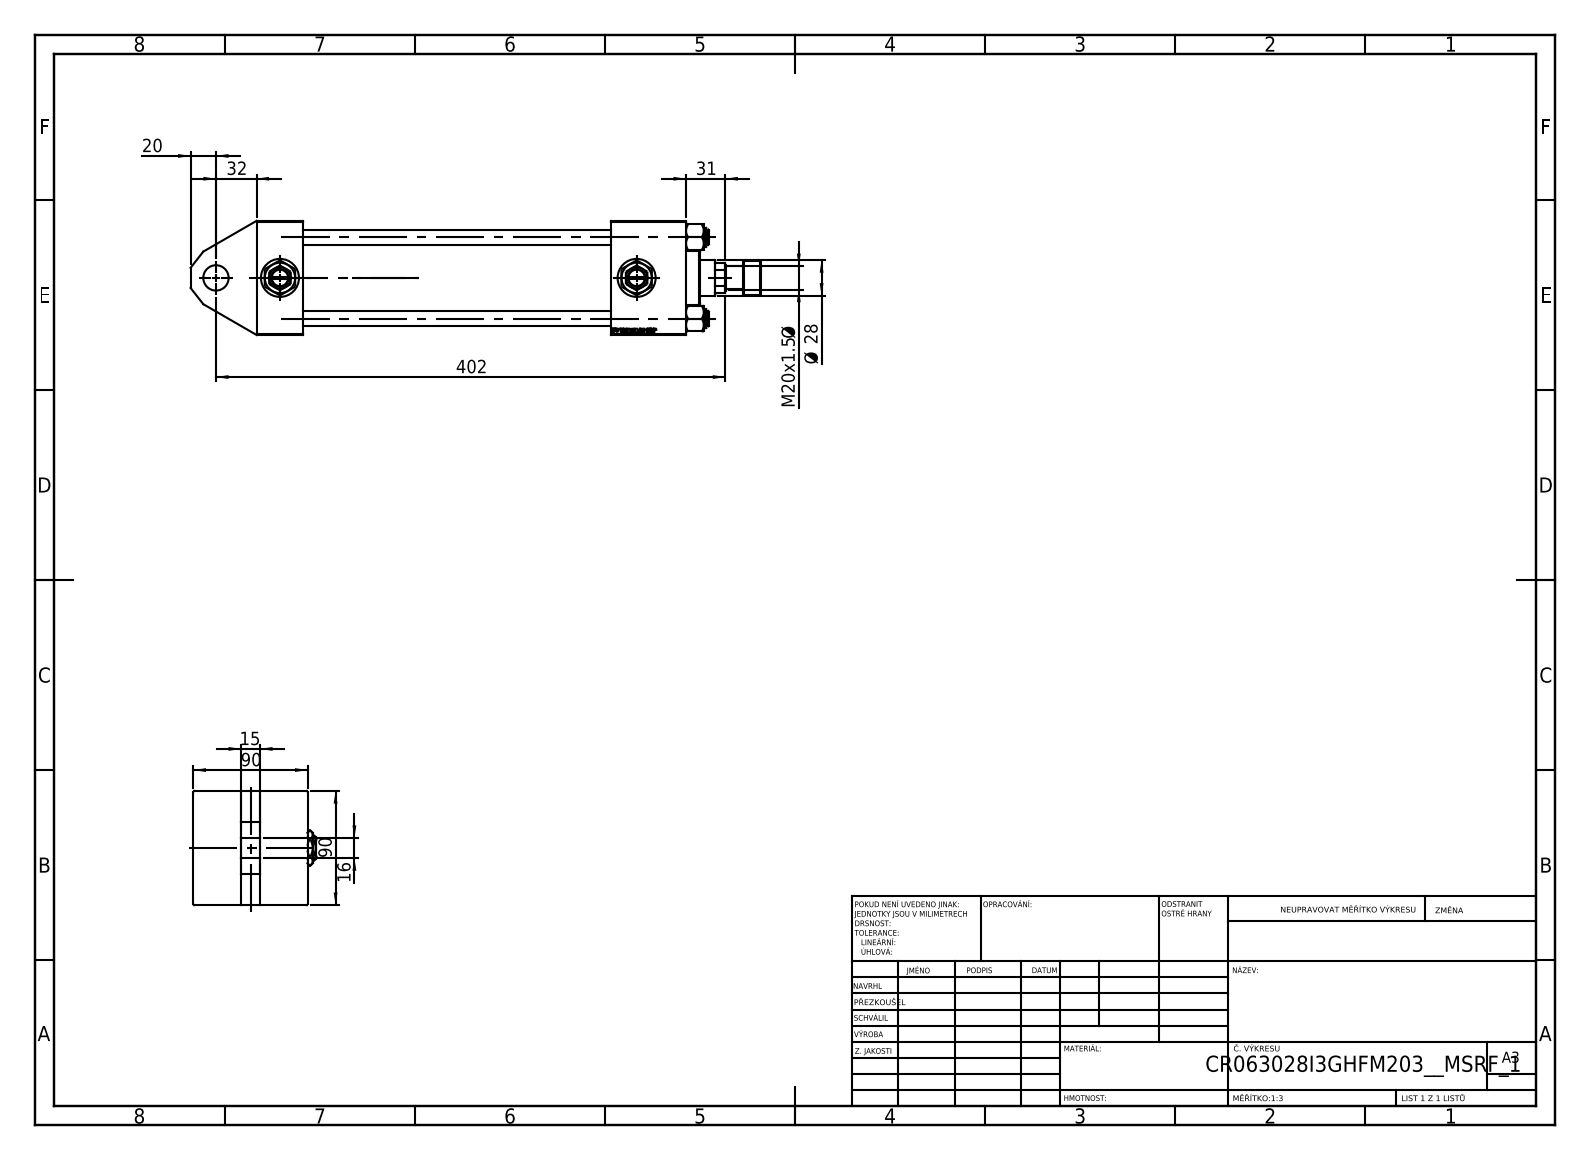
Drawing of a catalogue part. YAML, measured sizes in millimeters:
part_name: "NUT_M5_I; Zatka_pro_OIL_PORT; V215CR_VCP_I; V215CR_TYCINKA_I (+3 more)"
step_written_by: "SolidWorks 2019 (CONFIG_CONTROL_DESIGN)"
units: millimeters
bodies: {solids: 14, faces: 1194, planar: 554, cylindrical: 96, other: 544}
overall_size: [450, 97, 90]
volume: 1315000
surface_area: 317773
round_holes:
  - {diameter: 12, count: 4}
  - {diameter: 7, count: 2}
  - {diameter: 20.96, count: 2}
  - {diameter: 30, count: 2}
  - {diameter: 18.5, count: 1}
  - {diameter: 20, count: 1}
  - {diameter: 28, count: 1}
  - {diameter: 31, count: 1}
  - {diameter: 50, count: 1}
  - {diameter: 60, count: 1}
  - {diameter: 63, count: 1}
round_bosses_or_shafts:
  - {diameter: 15, count: 4}
  - {diameter: 69, count: 1}
  - {diameter: 42, count: 1}
  - {diameter: 27, count: 1}
  - {diameter: 18, count: 1}
face_to_face_distances: [90, 37, 339, 302, 59, 37.5, 52.5, 280, 243, 310.3]
hole_center_spacings: [45.47, 64.3, 90.93, 50.5, 281.5, 332]
